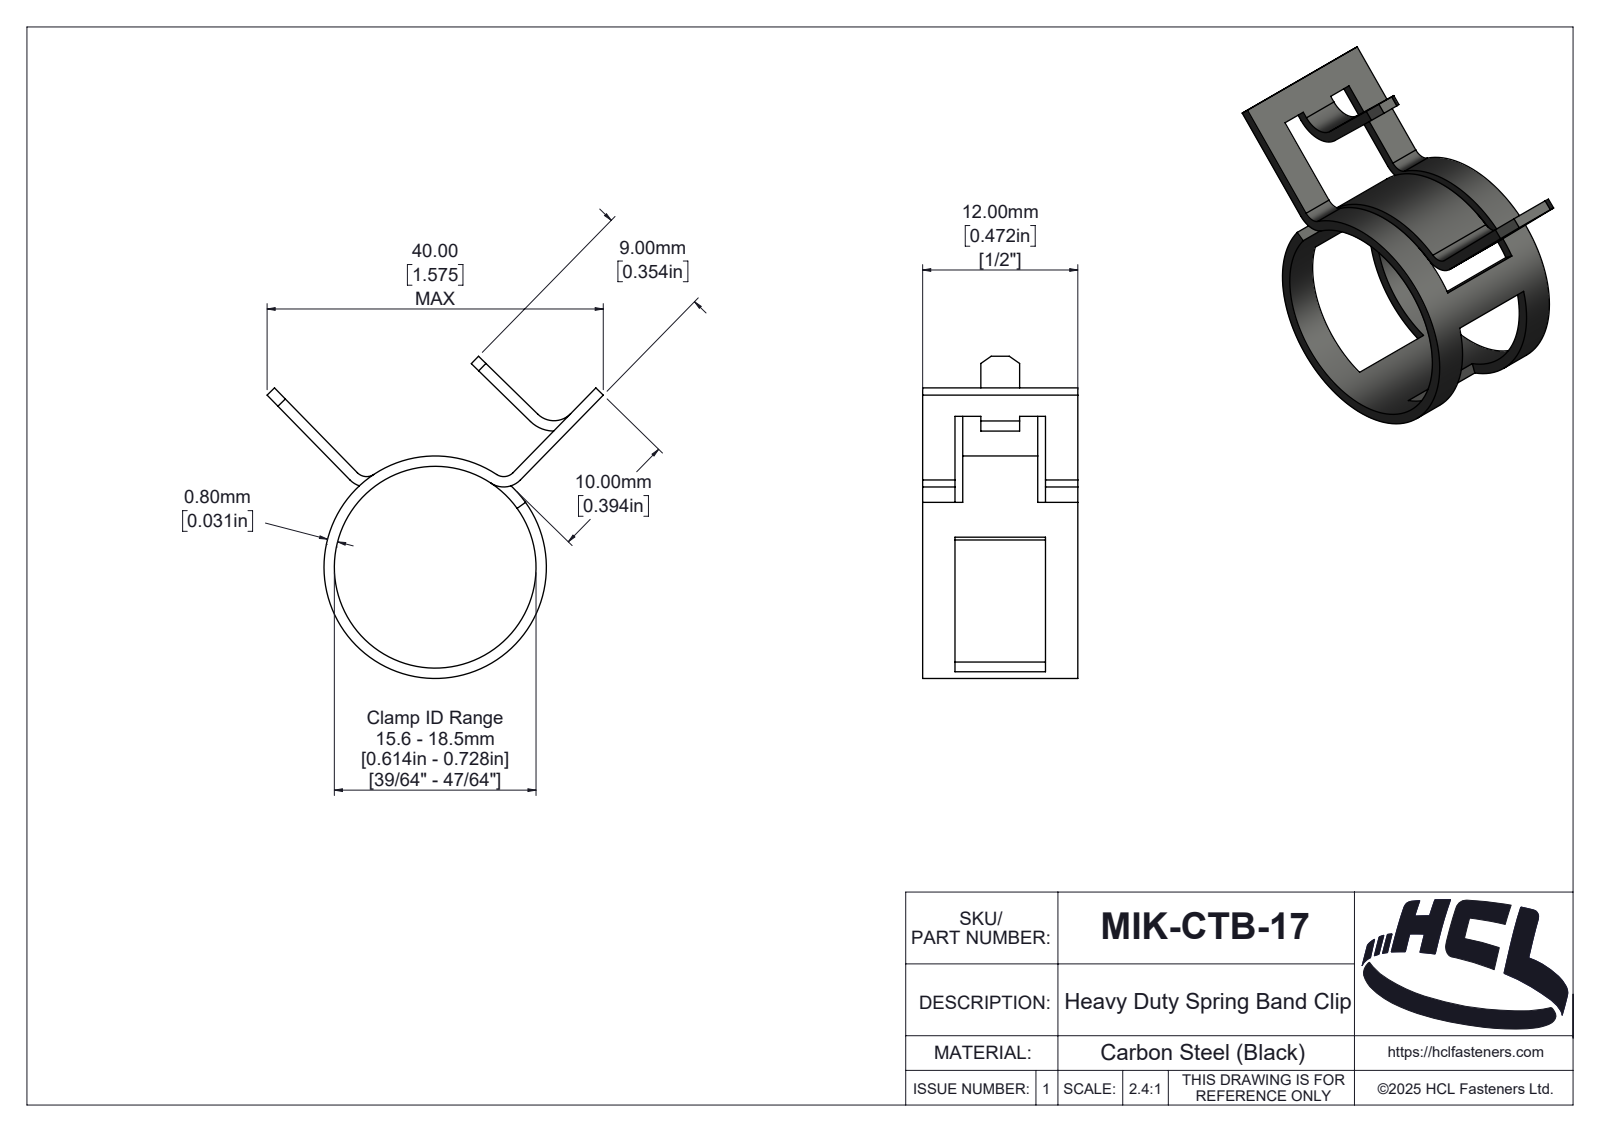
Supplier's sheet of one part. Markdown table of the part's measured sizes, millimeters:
| quantity | value |
| --- | --- |
| part name | MIK-CTB-17 |
| STEP written by | SolidWorks 2025 (AUTOMOTIVE_DESIGN) |
| units | millimeters |
| bodies | 1 solid, 149 faces (36 planar, 64 cylindrical, 49 other) |
| overall size | 26 × 24.91 × 12 |
| volume | 447 mm³ |
| surface area | 1 402 mm² |
| round holes (diameter × count) | 15.6 × 1 |
| round bosses / shafts (diameter × count) | 17.2 × 1 |
| partial cylindrical surfaces (radius × count) | 1.8 × 3, 1 × 2, 0.33 × 1, 1.35 × 1, 1.68 × 1, 1.77 × 1, 2.14 × 1, 2.6 × 1 |
| main face-to-face distances | 0.8, 2.5, 9.5, 12, 3.1, 7, 8.9, 0.6, 6.4, 5.8 |
